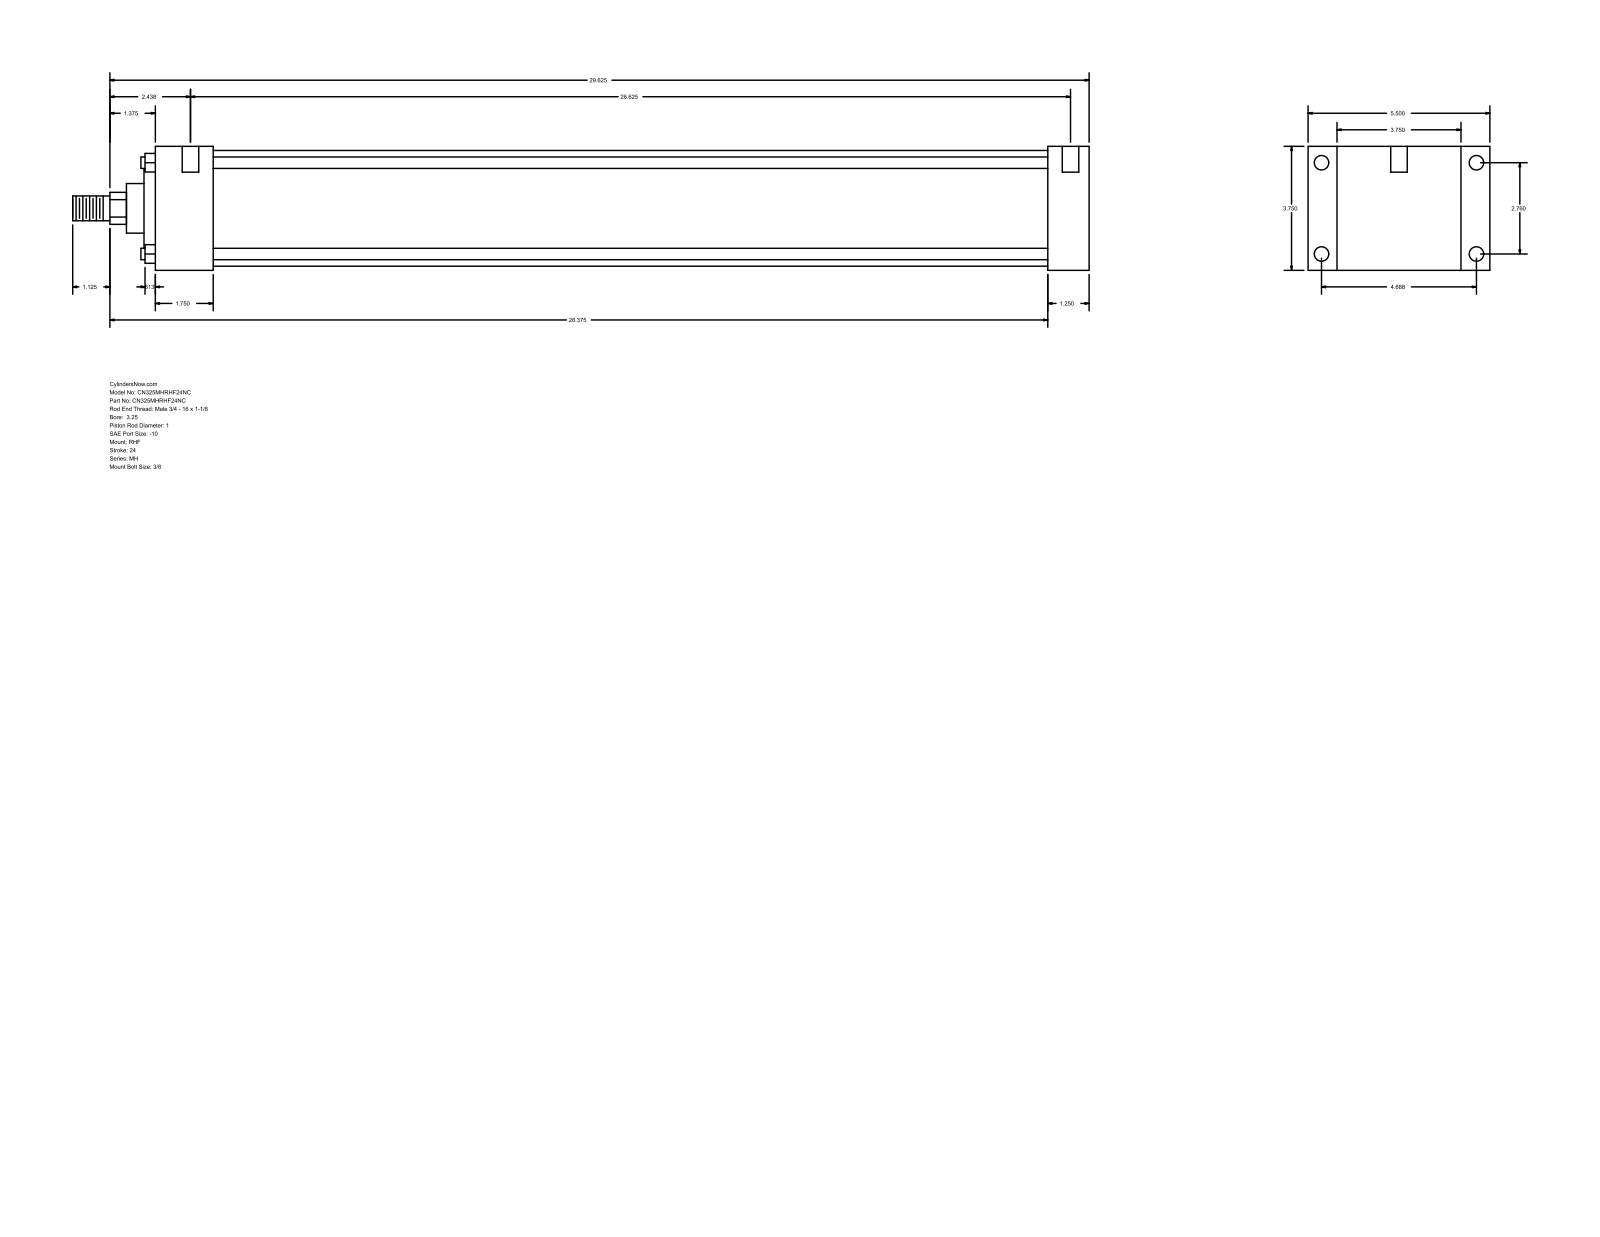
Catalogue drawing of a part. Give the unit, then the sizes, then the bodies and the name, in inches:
Units: inches
Overall size (bounding box): 30.75 × 5.5 × 3.75
Round holes (diameter × count): ⌀0.219 ×4, ⌀0.438 ×4, ⌀0.5 ×2
Round bosses / shafts (diameter × count): ⌀0.345 ×4, ⌀3.5 ×1, ⌀2.375 ×1, ⌀1.5 ×1, ⌀1 ×1, ⌀0.75 ×1
Partial cylindrical surfaces — rounded edges, fillets, slot ends (radius × count): R0.484 ×1
Main face-to-face distances: 3.75, 1.25, 0.875, 4.625, 27, 28.25, 5.5, 1.75, 25.25, 26.5
Hole centre spacings: 2.76, 4.687, 5.439, 26.875, 0.062, 0.187, 26.625, 26.687
Bodies: 0 solids, 90 faces (61 planar, 29 cylindrical, 0 other)
Part name (STEP PRODUCT): MH_RHF__0325_1
STEP written by: GSSL Pune (CONFIG_CONTROL_DESIGN)
